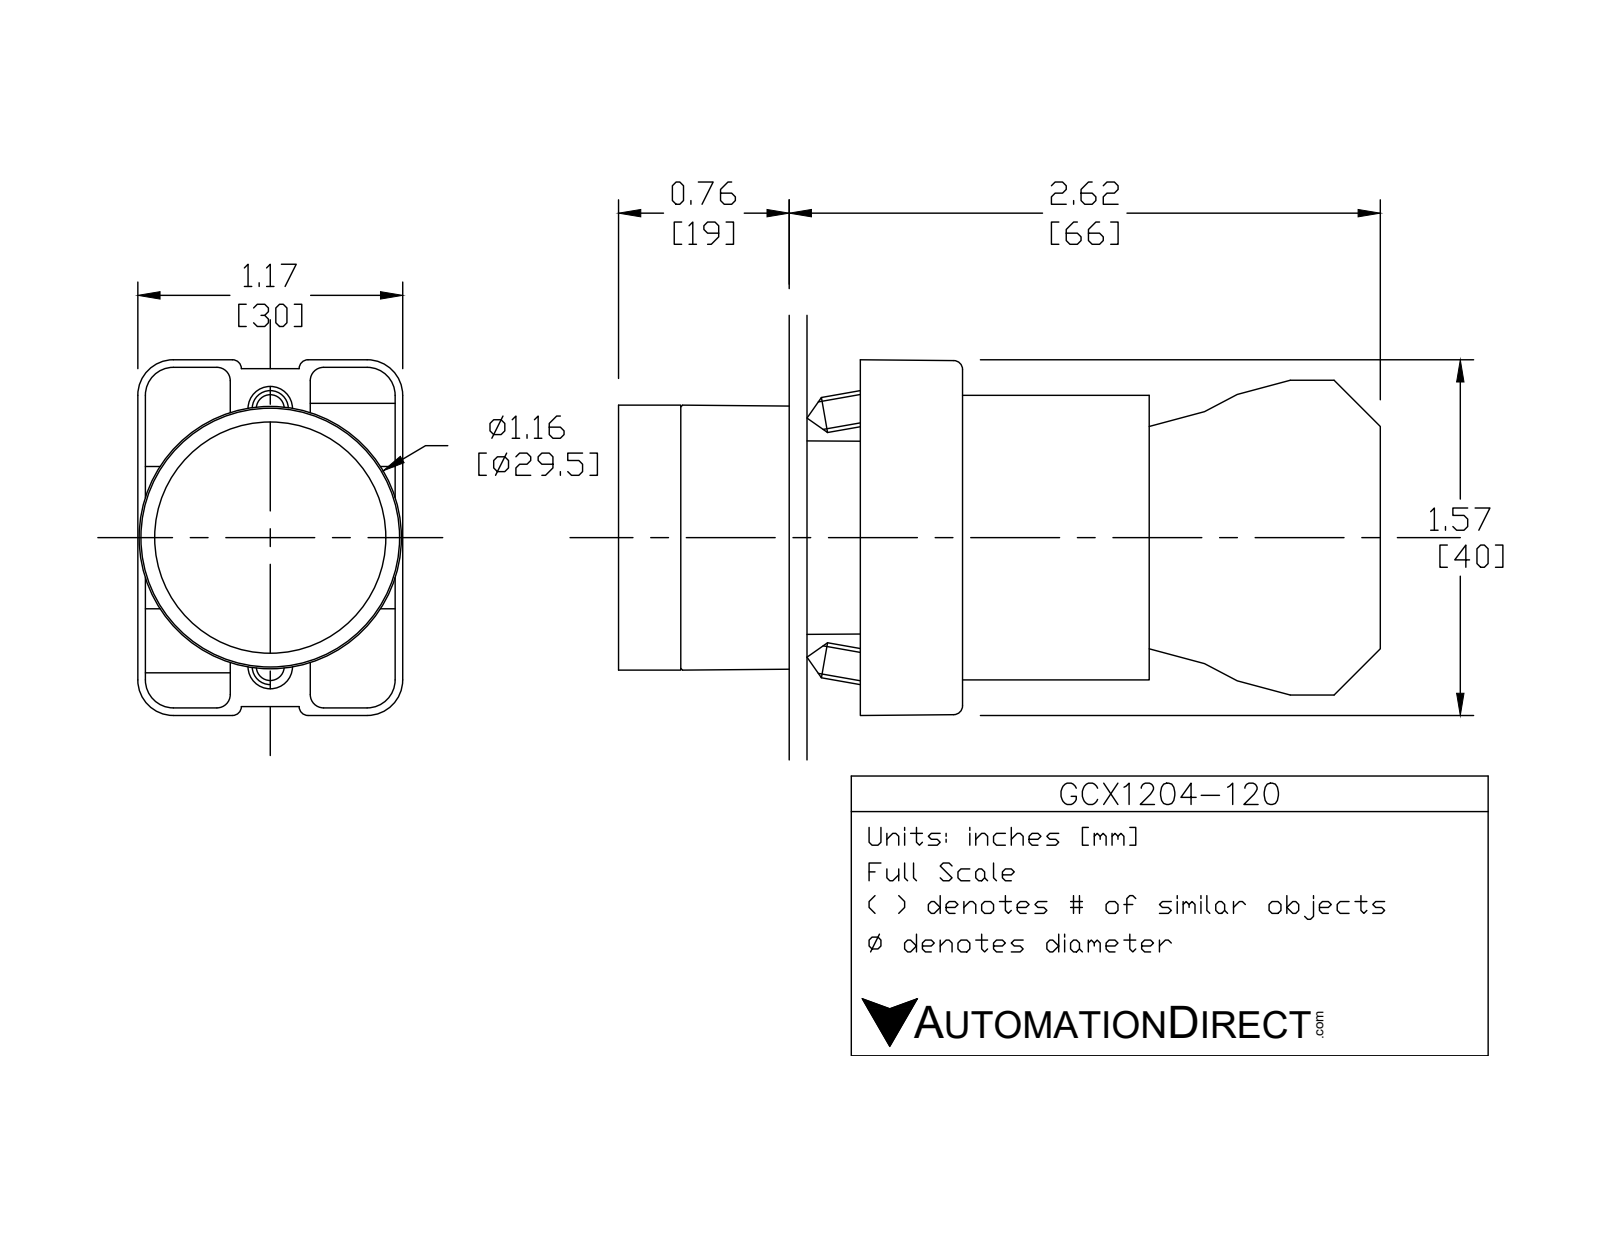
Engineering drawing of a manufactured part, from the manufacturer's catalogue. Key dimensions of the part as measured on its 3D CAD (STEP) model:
Part name (STEP PRODUCT): ecx1040; GCX1204-120; ECX1050; ecx1029 (+1 more)
STEP written by: SolidWorks 2016 (AUTOMOTIVE_DESIGN)
Units: inches
Bodies: 8 solids, 431 faces (252 planar, 148 cylindrical, 31 other)
Overall size (bounding box): 3.319 × 1.581 × 1.177
Volume: 2.794 in³ · Surface area: 38.75 in²
Round holes (diameter × count): ⌀0.079 ×2, ⌀0.124 ×2, ⌀0.13 ×2, ⌀0.087 ×1, ⌀0.197 ×1, ⌀0.469 ×1, ⌀0.878 ×1, ⌀0.888 ×1, ⌀1.024 ×1
Round bosses / shafts (diameter × count): ⌀0.157 ×4, ⌀1.175 ×1, ⌀1.004 ×1, ⌀0.945 ×1, ⌀0.856 ×1, ⌀0.78 ×1, ⌀0.504 ×1
Partial cylindrical surfaces — rounded edges, fillets, slot ends (radius × count): R0.059 ×24, R0.041 ×12, R0.124 ×12, R0.157 ×12, R0.039 ×8, R0.128 ×2, R0.02 ×1, R0.063 ×1
Main face-to-face distances: 0.827, 2.02, 1.193, 0.579, 1.171, 0.031, 0.276, 0.033, 0.748, 0.573
Hole centre spacings: 0.236, 0.544, 0.472, 0.49
